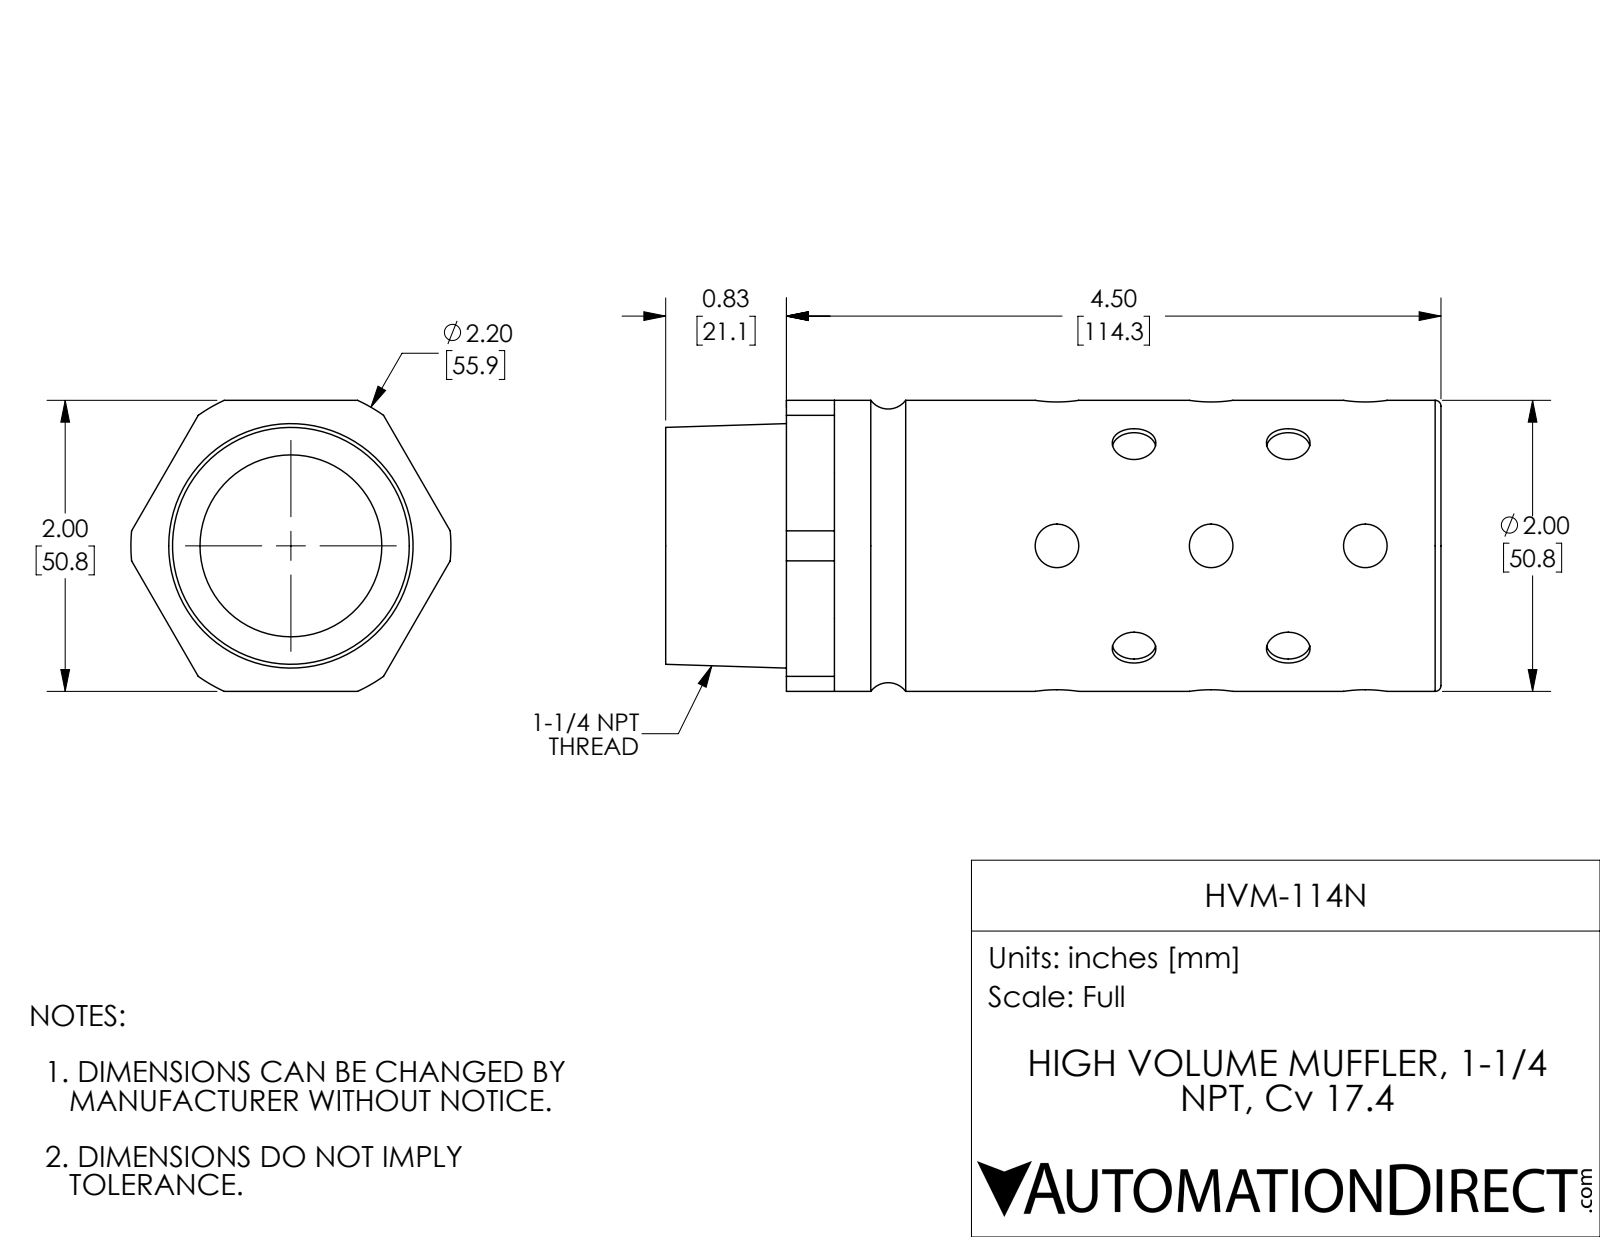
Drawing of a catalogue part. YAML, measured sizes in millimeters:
part_name: "HVM-114N"
step_written_by: "SolidWorks 2017 (AUTOMOTIVE_DESIGN)"
units: millimeters
bodies: {solids: 1, faces: 97, planar: 36, cylindrical: 53, other: 8}
overall_size: [135.4, 55.9, 50.8]
volume: 158200
surface_area: 38910
round_holes:
  - {diameter: 7.6, count: 14}
  - {diameter: 31.8, count: 1}
round_bosses_or_shafts:
  - {diameter: 50.8, count: 1}
partial_cylinders:
  - {radius: 27.9, count: 1}
face_to_face_distances: [6.4, 108, 114.3, 50.8, 21.1, 129, 135.4, 48.3, 1.3, 49.5]
hole_center_spacings: [26.9, 26.9, 53.8]
